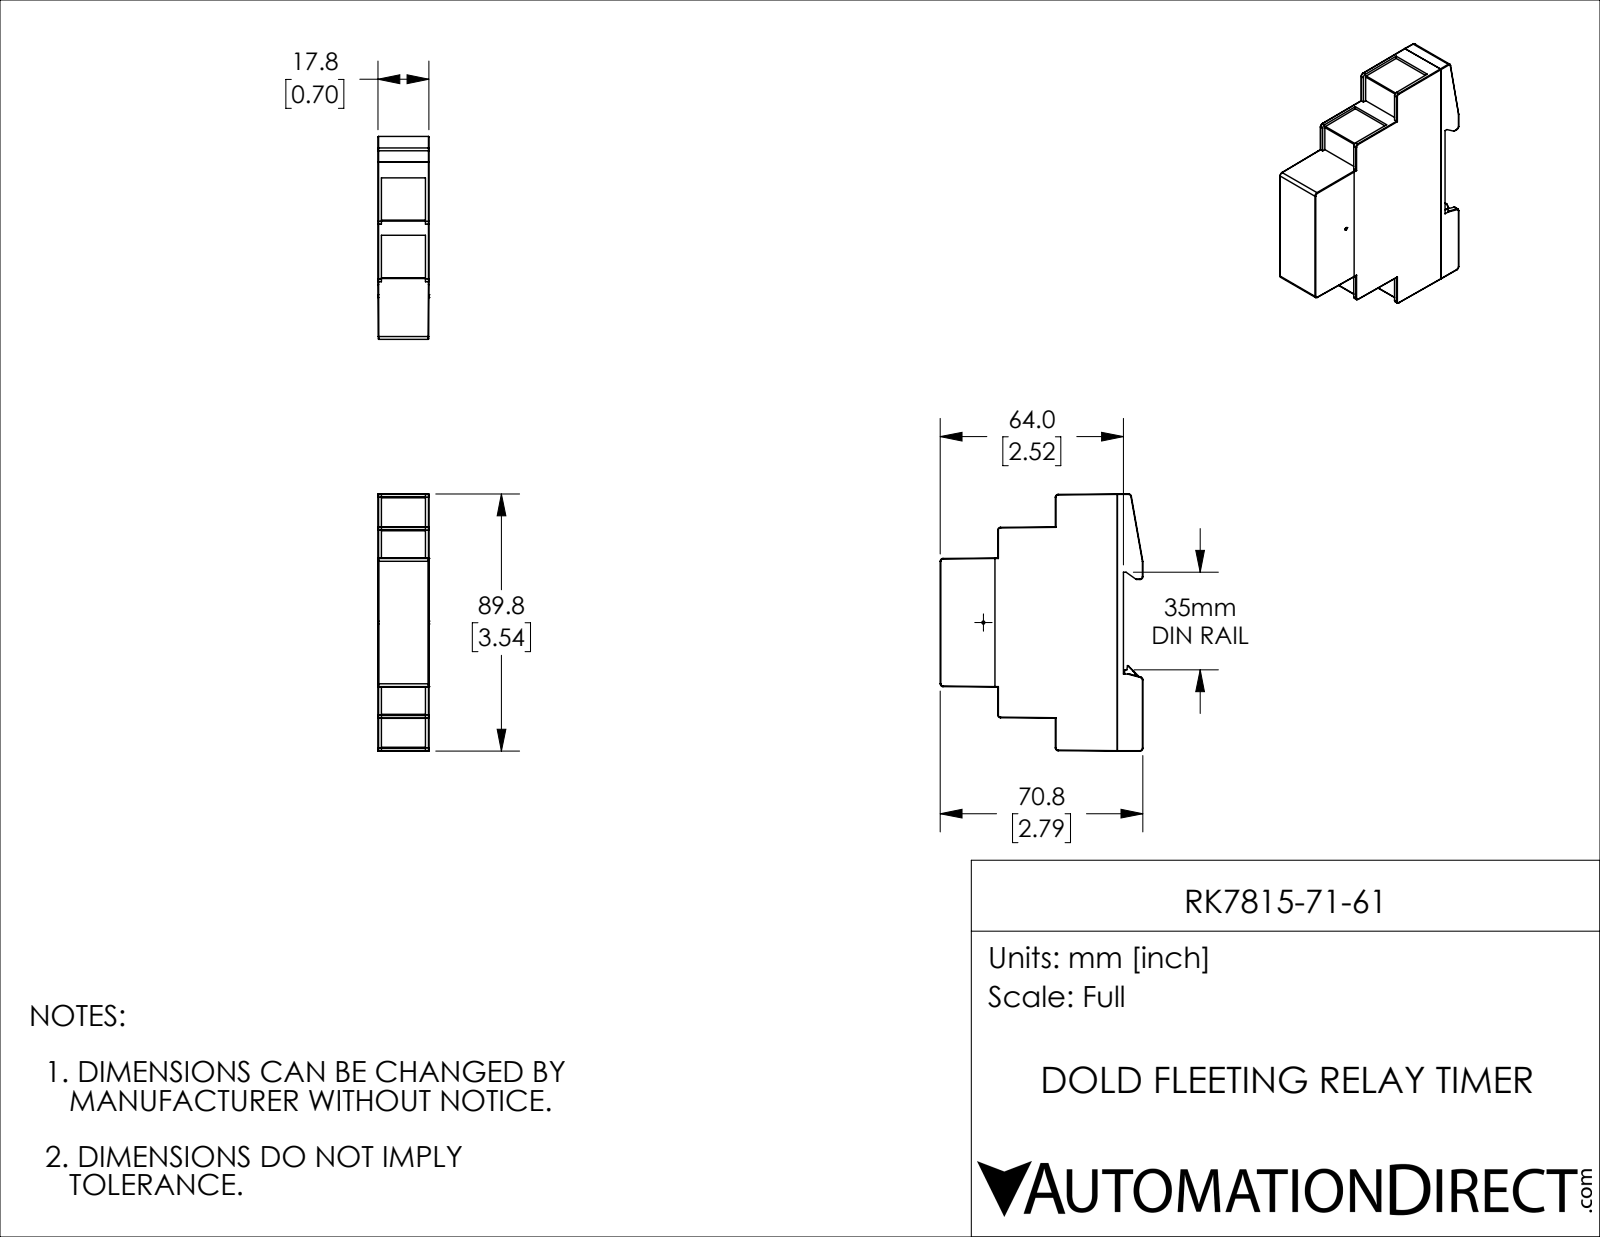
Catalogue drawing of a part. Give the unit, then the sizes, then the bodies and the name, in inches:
Units: inches
Overall size (bounding box): 3.535 × 2.787 × 0.701
Round bosses / shafts (diameter × count): ⌀0.039 ×1
Partial cylindrical surfaces — rounded edges, fillets, slot ends (radius × count): R0.008 ×36, R0.039 ×12, R0.004 ×9, R0.012 ×4, R0.02 ×2, R0.011 ×1, R0.031 ×1, R0.118 ×1
Main face-to-face distances: 0.701, 0.085, 2.52, 2.435, 0.383, 0.446, 0.829, 0.791, 0.835, 0.894
Volume: 4.945 in³ · Surface area: 31.16 in²
Bodies: 3 solids, 267 faces (158 planar, 85 cylindrical, 24 other)
Part name (STEP PRODUCT): RK7815-71-61
STEP written by: SolidWorks 2019 (CONFIG_CONTROL_DESIGN)
